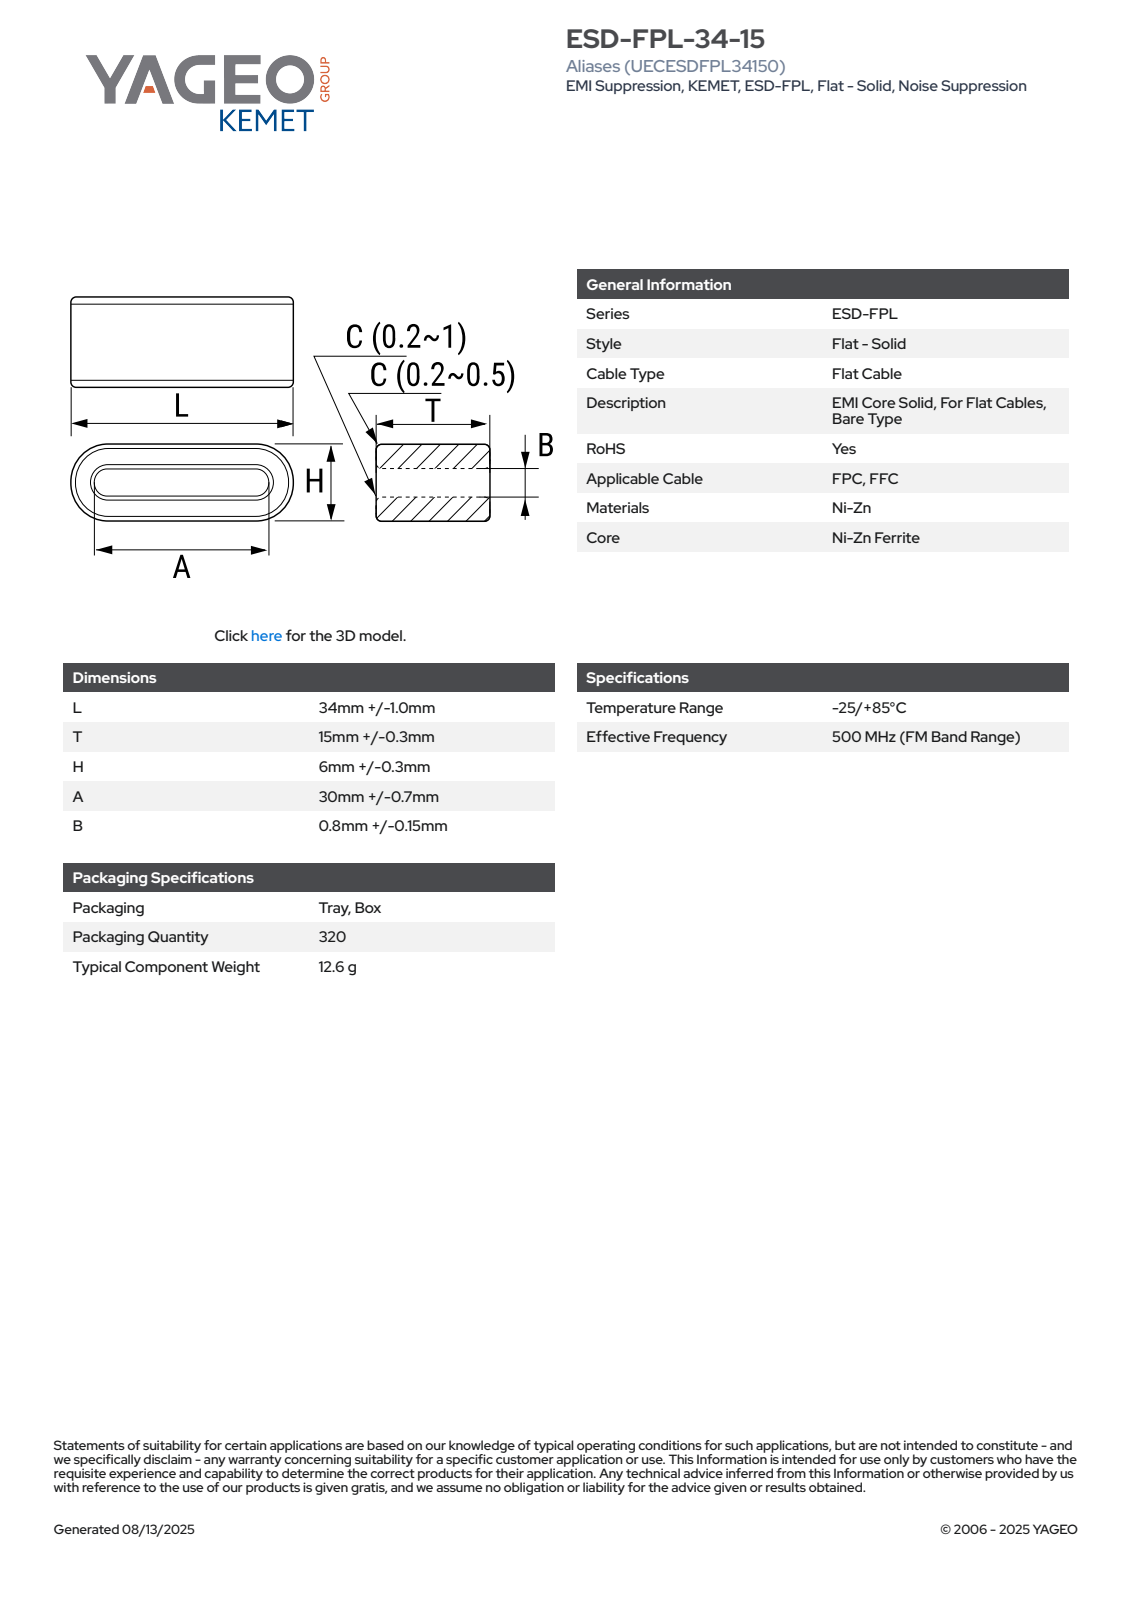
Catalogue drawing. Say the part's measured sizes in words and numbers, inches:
The part is named "EC_FPL3_L35T15.3H6.3A30B0.8". Its 3-D file was written by "SolidWorks 2021 (AUTOMOTIVE_DESIGN)". It is 4 solids with 95 faces: 63 planar, 16 cylindrical and 16 other. Overall it measures 1.378 by 0.602 by 0.248 inches. Its volume is 0.176 cubic inches and its surface area 3.86 square inches. Partial cylindrical surfaces (rounded edges, fillets, slot ends): 8 of radius 0.008, 2 of radius 0.016, 2 of radius 0.124. The main face-to-face distances are 0.108, 0.14, 0.031, 0.248, 0.602, 0.261, 0.341, 0.08, 0.277, 0.326.
